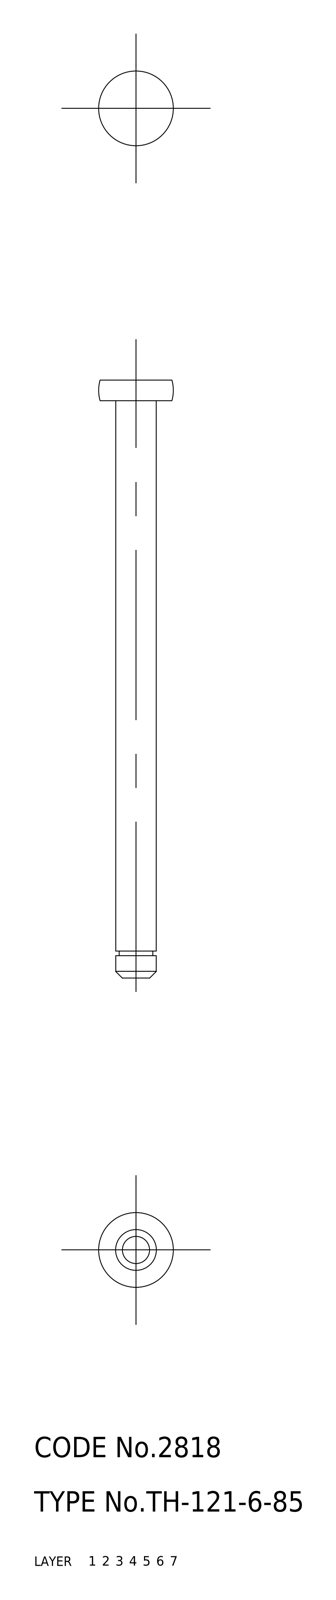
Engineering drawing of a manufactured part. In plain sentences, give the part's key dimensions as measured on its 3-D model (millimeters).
The part is named "shaft". Its 3-D file was written by "CADfix (AUTOMOTIVE_DESIGN)". It is 1 solid with 14 faces: 0 planar, 0 cylindrical and 14 other. Overall it measures 88 by 11 by 11 millimeters. Its volume is 2 671 cubic millimeters and its surface area 1 886 square millimeters.
